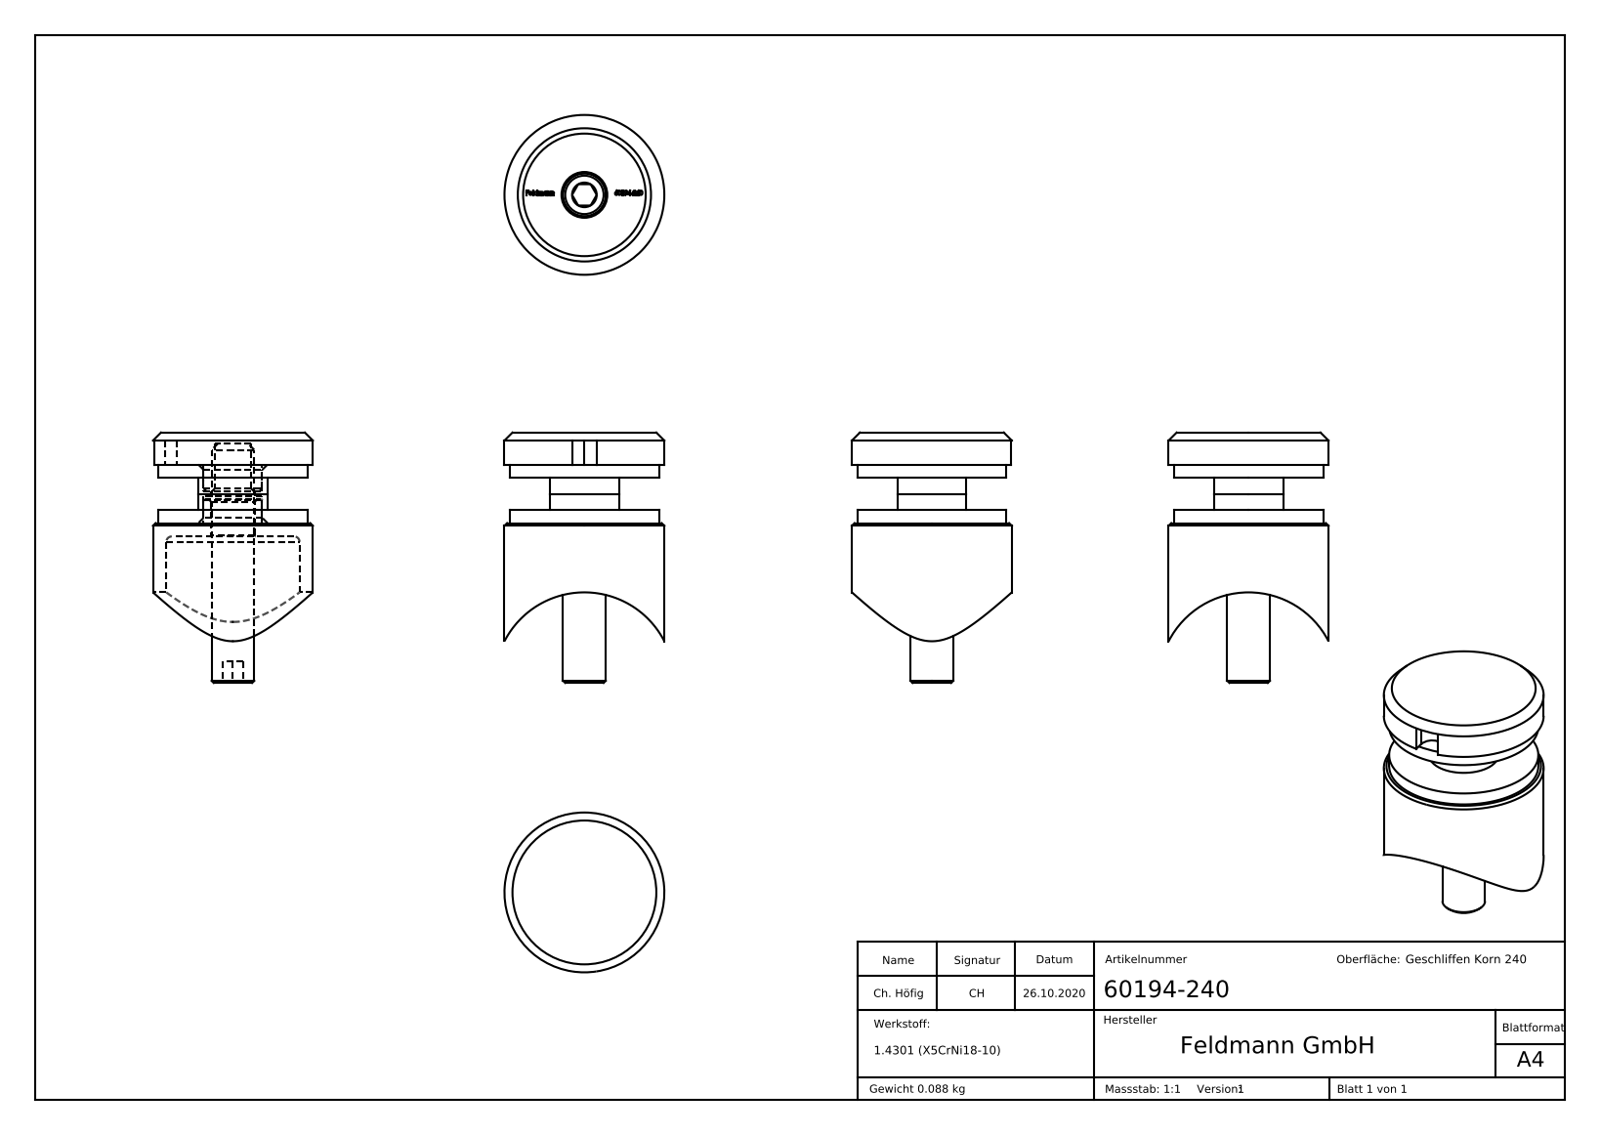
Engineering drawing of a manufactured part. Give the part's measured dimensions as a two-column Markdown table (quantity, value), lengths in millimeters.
| quantity | value |
| --- | --- |
| part name | 6019X-240 Teil3_6019X-240 Teil3; 6019X-240 Teil3; 60190-240 Teil1; 60190-240 Teil1_6019X-240 Teil1 (+5 more) |
| STEP written by | SolidWorks 2018 (CONFIG_CONTROL_DESIGN) |
| units | millimeters |
| bodies | 5 solids, 306 faces (155 planar, 35 cylindrical, 116 other) |
| overall size | 47 × 30 × 30 |
| volume | 13 946 mm³ |
| surface area | 11 081 mm² |
| round holes (diameter × count) | 6.8 × 1, 8.2 × 1, 11 × 1, 25 × 1 |
| round bosses / shafts (diameter × count) | 30 × 1, 28 × 1, 13 × 1, 8 × 1 |
| partial cylindrical surfaces (radius × count) | 2.25 × 1, 16.85 × 1 |
| main face-to-face distances | 11, 2.4, 8.6, 6, 17, 8.4, 6.2, 14.6, 2.5, 4.9 |
